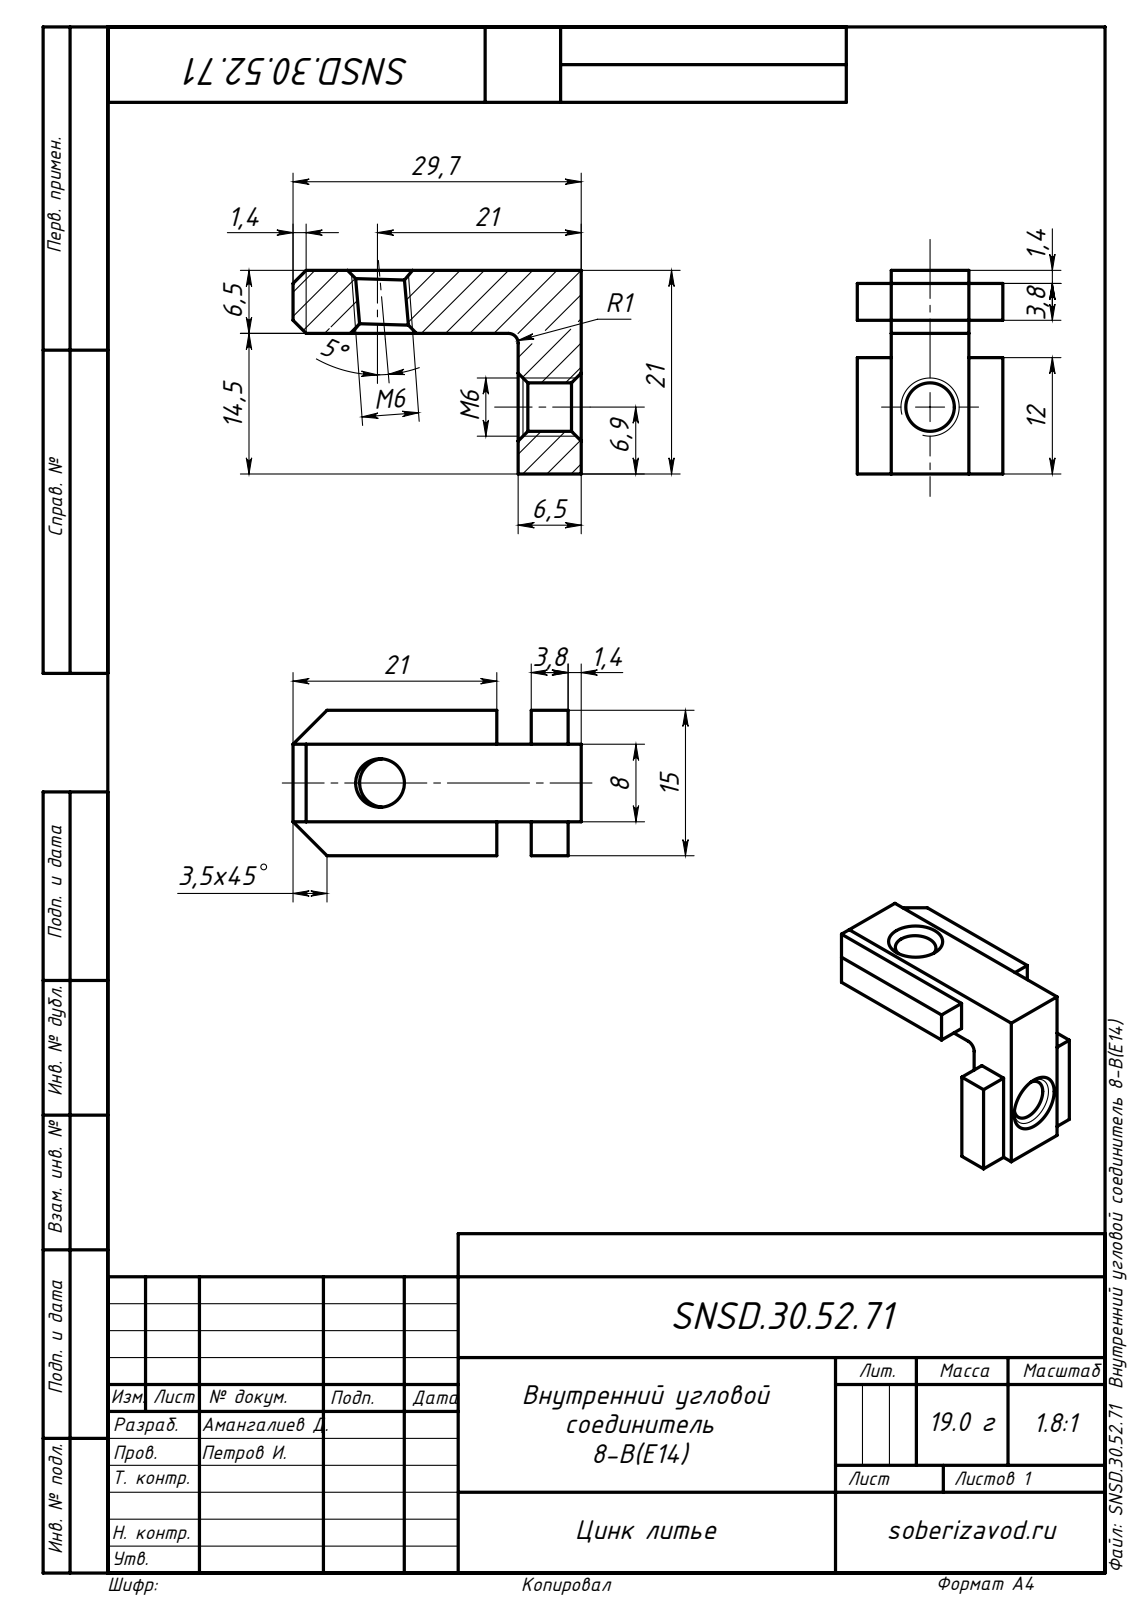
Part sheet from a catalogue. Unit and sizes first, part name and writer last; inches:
Units: inches
Overall size (bounding box): 1.169 × 0.827 × 0.591
Round holes (diameter × count): ⌀0.197 ×2
Partial cylindrical surfaces — rounded edges, fillets, slot ends (radius × count): R0.039 ×1
Main face-to-face distances: 0.053, 0.203, 0.138, 0.453, 0.15, 0.256, 0.315, 0.591, 0.827, 0.774
Volume: 0.173 in³ · Surface area: 3.086 in²
Bodies: 1 solid, 41 faces (28 planar, 5 cylindrical, 8 other)
Part name (STEP PRODUCT): SNSD.30.52.71 Внутренний угловой соединитель 8-B(E14)
STEP written by: SolidWorks 2014 (AUTOMOTIVE_DESIGN)
